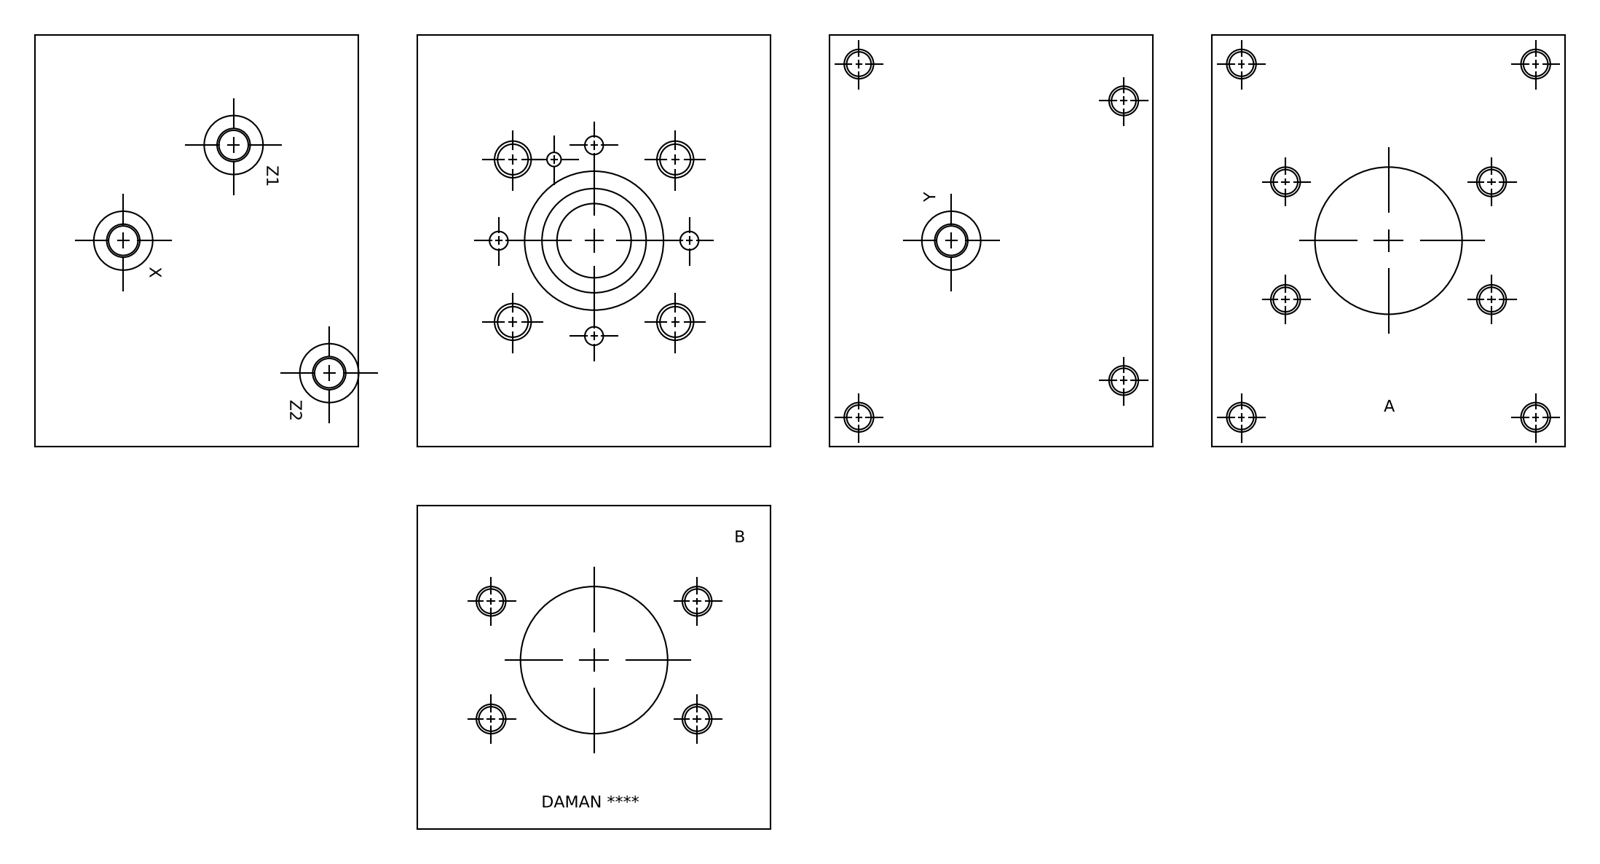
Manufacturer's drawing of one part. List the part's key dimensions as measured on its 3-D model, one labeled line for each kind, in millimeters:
Part name (STEP PRODUCT): Part_D32XA40F61_3D
STEP written by: Autodesk Inventor 2020 (CONFIG_CONTROL_DESIGN)
Units: millimetres
Bodies: 1 solid, 569 faces (365 planar, 68 cylindrical, 136 other)
Overall size (bounding box): 177.8 × 152.4 × 139.7
Volume: 3 283 000 mm³ · Surface area: 204 828 mm²
Round holes (diameter × count): ⌀10.72 ×16, ⌀12.7 ×16, ⌀12.29 ×4, ⌀12.9 ×4, ⌀13.49 ×4, ⌀14.27 ×4, ⌀14.53 ×4, ⌀15.88 ×4, ⌀25.02 ×4, ⌀63.5 ×2, ⌀5.99 ×1, ⌀32 ×1
Main face-to-face distances: 152.4, 139.7, 177.8, 70, 0.79, 151.61, 69.7, 54.71, 14.99, 84.99
Hole centre spacings: 51.2, 49.5, 50.1, 61.13, 70, 99.19, 106.77, 114.79
